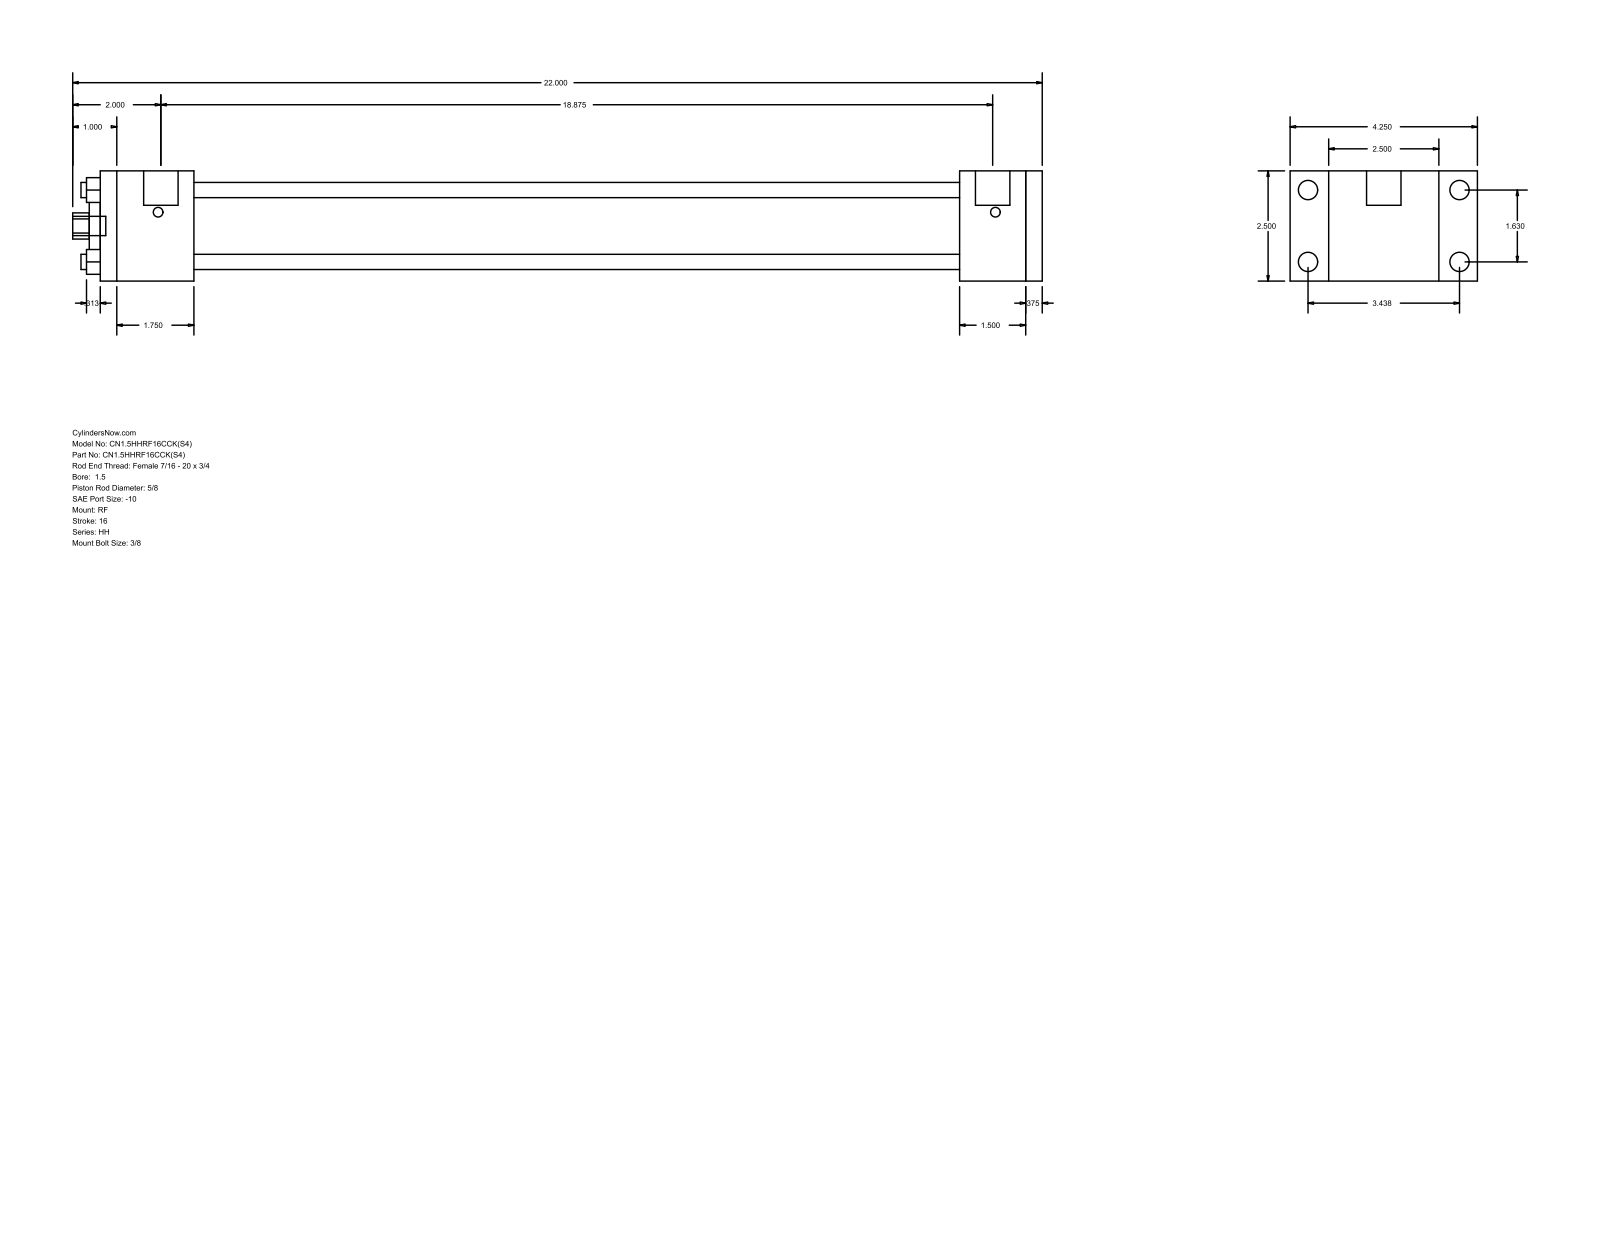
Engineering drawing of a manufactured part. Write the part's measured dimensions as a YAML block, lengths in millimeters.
part_name: "HH_RF__0150_0.625"
step_written_by: "GSSL Pune (CONFIG_CONTROL_DESIGN)"
units: millimeters
bodies: {solids: 0, faces: 92, planar: 64, cylindrical: 28, other: 0}
overall_size: [558.8, 107.95, 63.5]
round_holes:
  - {diameter: 8.76, count: 4}
  - {diameter: 15.88, count: 1}
  - {diameter: 28.57, count: 1}
  - {diameter: 44.45, count: 1}
round_bosses_or_shafts:
  - {diameter: 11.13, count: 4}
  - {diameter: 5.56, count: 4}
  - {diameter: 19.84, count: 2}
  - {diameter: 11.11, count: 1}
partial_cylinders:
  - {radius: 7.54, count: 1}
face_to_face_distances: [63.5, 542.92, 9.53, 533.39, 53.97, 495.3, 441.33, 479.42, 488.95, 38.09]
hole_center_spacings: [29.27, 41.4, 58.55]
